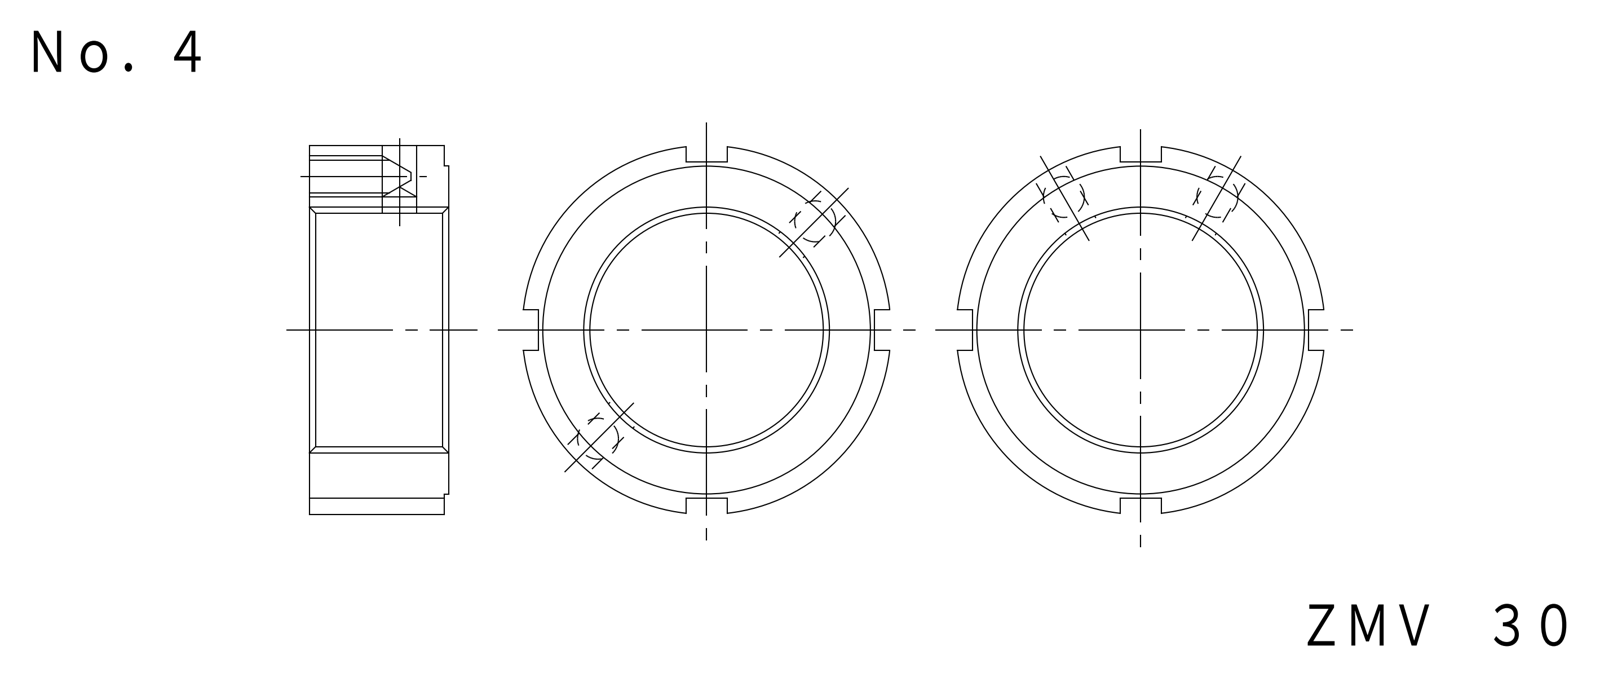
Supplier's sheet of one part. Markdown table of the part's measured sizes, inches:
| quantity | value |
| --- | --- |
| part name | FKD ZMV 30 |
| STEP written by | Autodesk Inventor 2011 (AUTOMOTIVE_DESIGN) |
| units | inches |
| bodies | 1 solid, 25 faces (15 planar, 10 cylindrical, 0 other) |
| overall size | 1.761 × 1.761 × 0.669 |
| volume | 0.839 in³ |
| surface area | 9.709 in² |
| round holes (diameter × count) | 0.163 × 2, 0.165 × 1, 1.181 × 1 |
| round bosses / shafts (diameter × count) | 1.772 × 1, 1.575 × 1 |
| main face-to-face distances | 0.669, 0.02, 0.65, 0.709, 0.906, 1.614, 0.197 |
| hole center spacings | 0.738, 1.476 |
